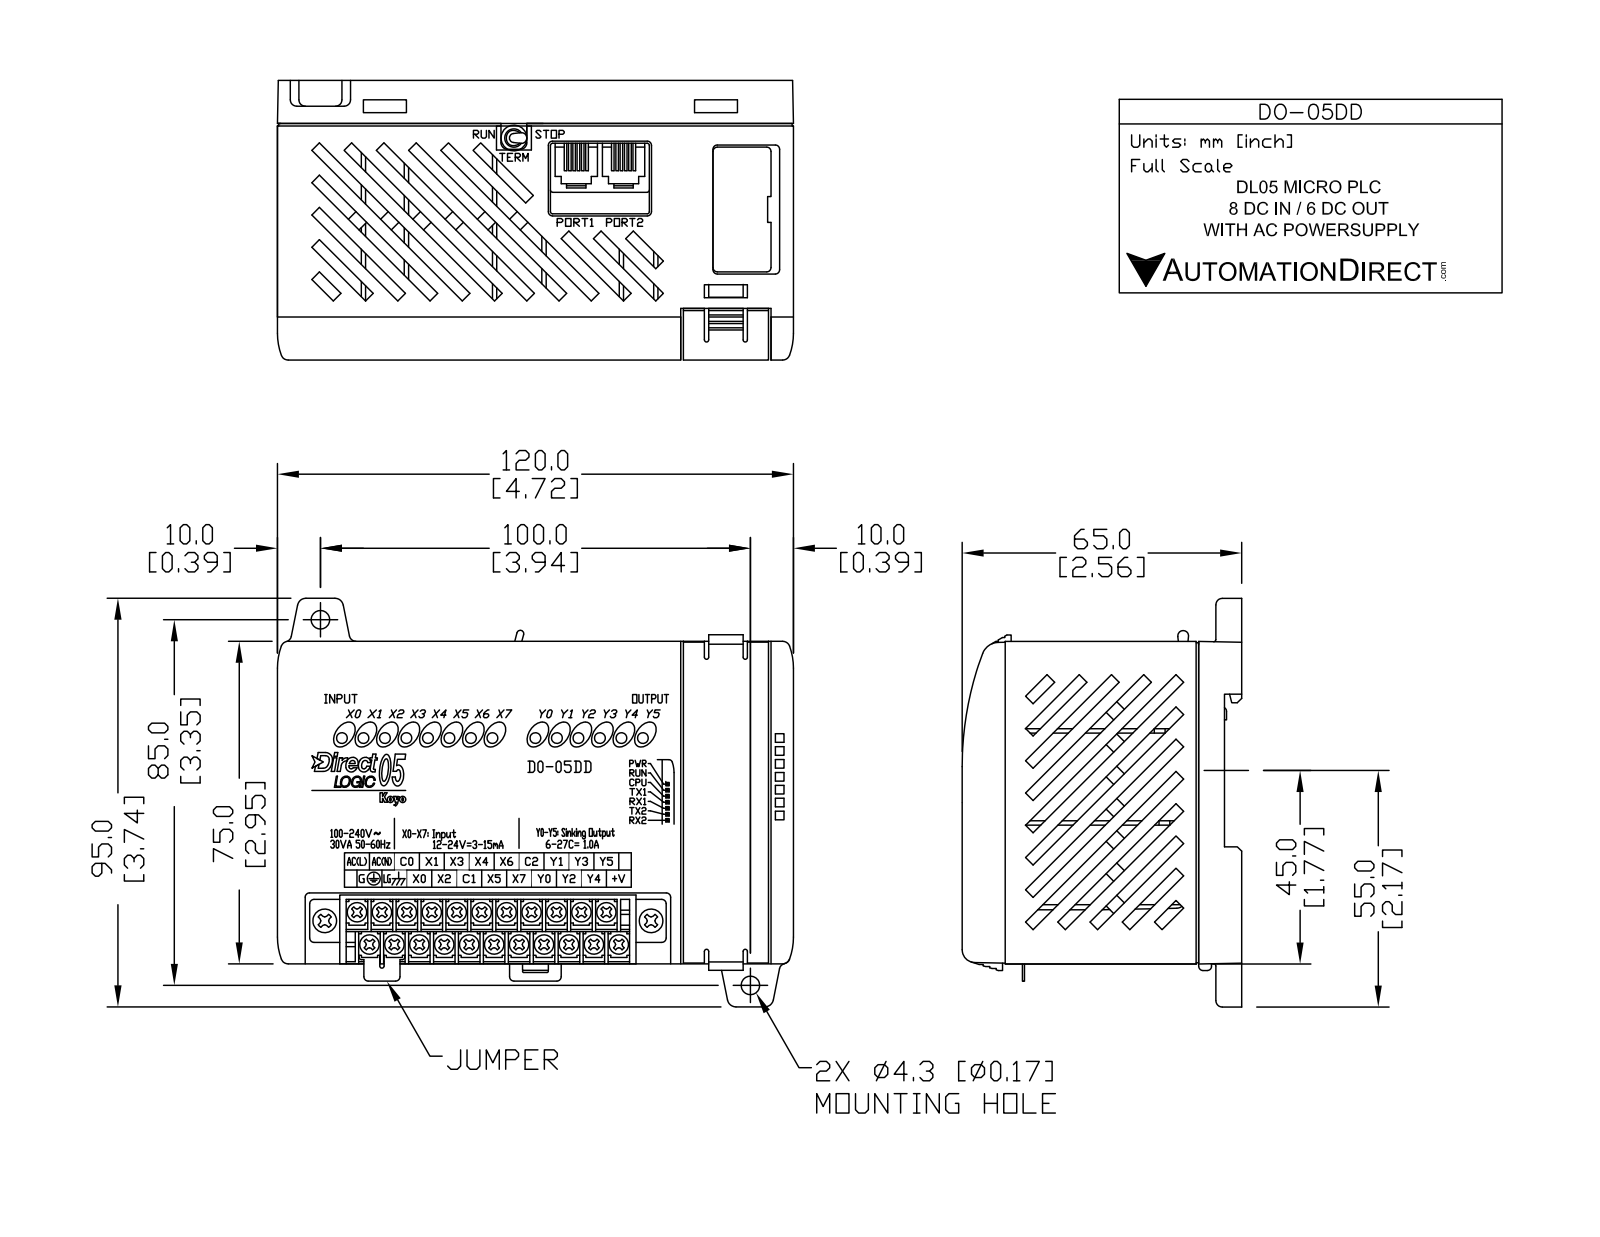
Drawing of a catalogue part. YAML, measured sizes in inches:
part_name: "D0-05DD"
step_written_by: "SolidWorks 2009 (AUTOMOTIVE_DESIGN)"
units: inches
bodies: {solids: 3, faces: 987, planar: 671, cylindrical: 95, other: 221}
overall_size: [4.724, 3.74, 2.561]
volume: 3.992
surface_area: 141.1
round_holes:
  - {diameter: 0.169, count: 2}
round_bosses_or_shafts:
  - {diameter: 0.174, count: 22}
  - {diameter: 0.177, count: 2}
partial_cylinders:
  - {radius: 0.039, count: 4}
  - {radius: 0.079, count: 4}
  - {radius: 0.059, count: 2}
  - {radius: 2.5, count: 1}
  - {radius: 2.559, count: 1}
face_to_face_distances: [0.059, 2.894, 2.343, 0.157, 2.5, 4.665, 2.953, 2.835, 0.217, 2.559]
hole_center_spacings: [5.167]
